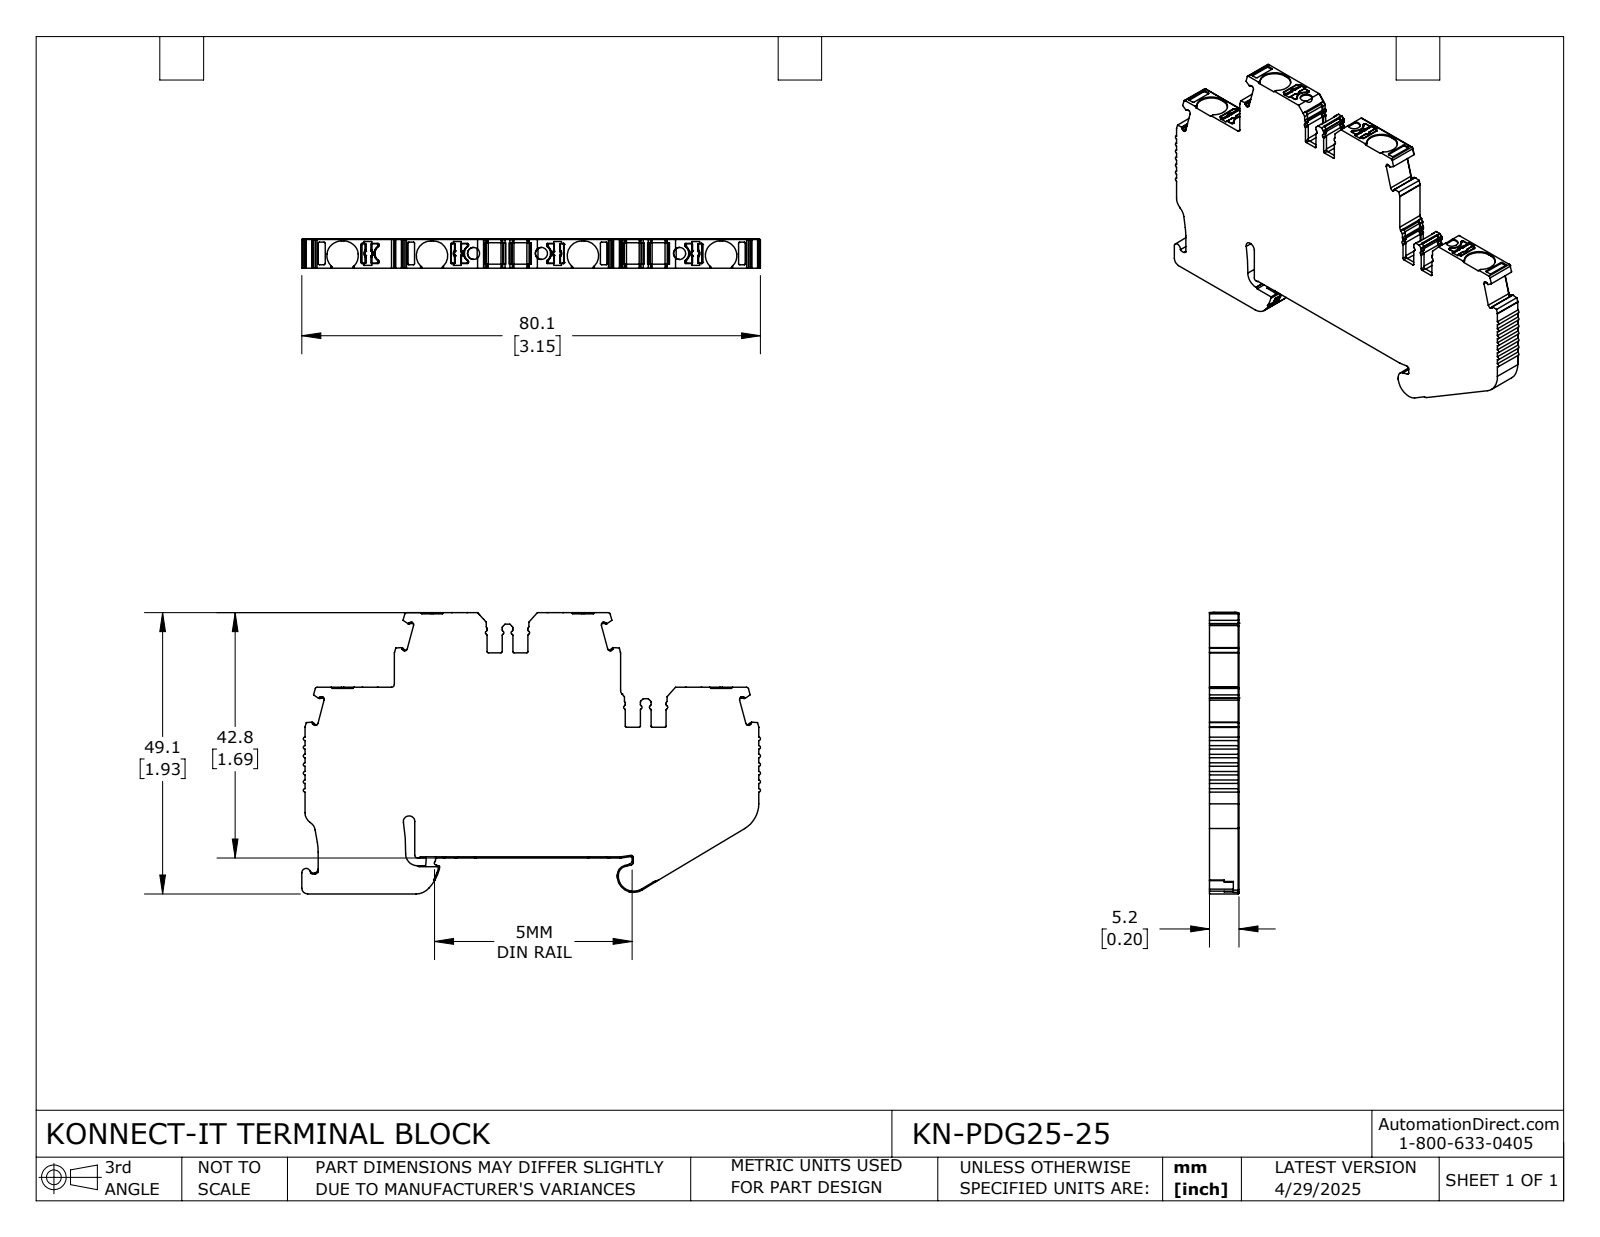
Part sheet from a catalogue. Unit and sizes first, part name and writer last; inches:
Units: inches
Overall size (bounding box): 3.153 × 1.933 × 0.203
Round holes (diameter × count): ⌀0.083 ×3
Partial cylindrical surfaces — rounded edges, fillets, slot ends (radius × count): R0.008 ×99, R0.012 ×59, R0.004 ×41, R0.016 ×25, R0.02 ×20, R0.006 ×16, R0.024 ×9, R0.039 ×9
Main face-to-face distances: 0.203, 0.512, 1.166, 1.678, 0.246, 1.924, 0.95, 1.412, 0.504, 0.254
Hole centre spacings: 0.466, 0.95, 1.417
Volume: 0.886 in³ · Surface area: 11.71 in²
Bodies: 1 solid, 1035 faces (499 planar, 463 cylindrical, 73 other)
Part name (STEP PRODUCT): KN-PDG25-25
STEP written by: SolidWorks 2024 (CONFIG_CONTROL_DESIGN)
